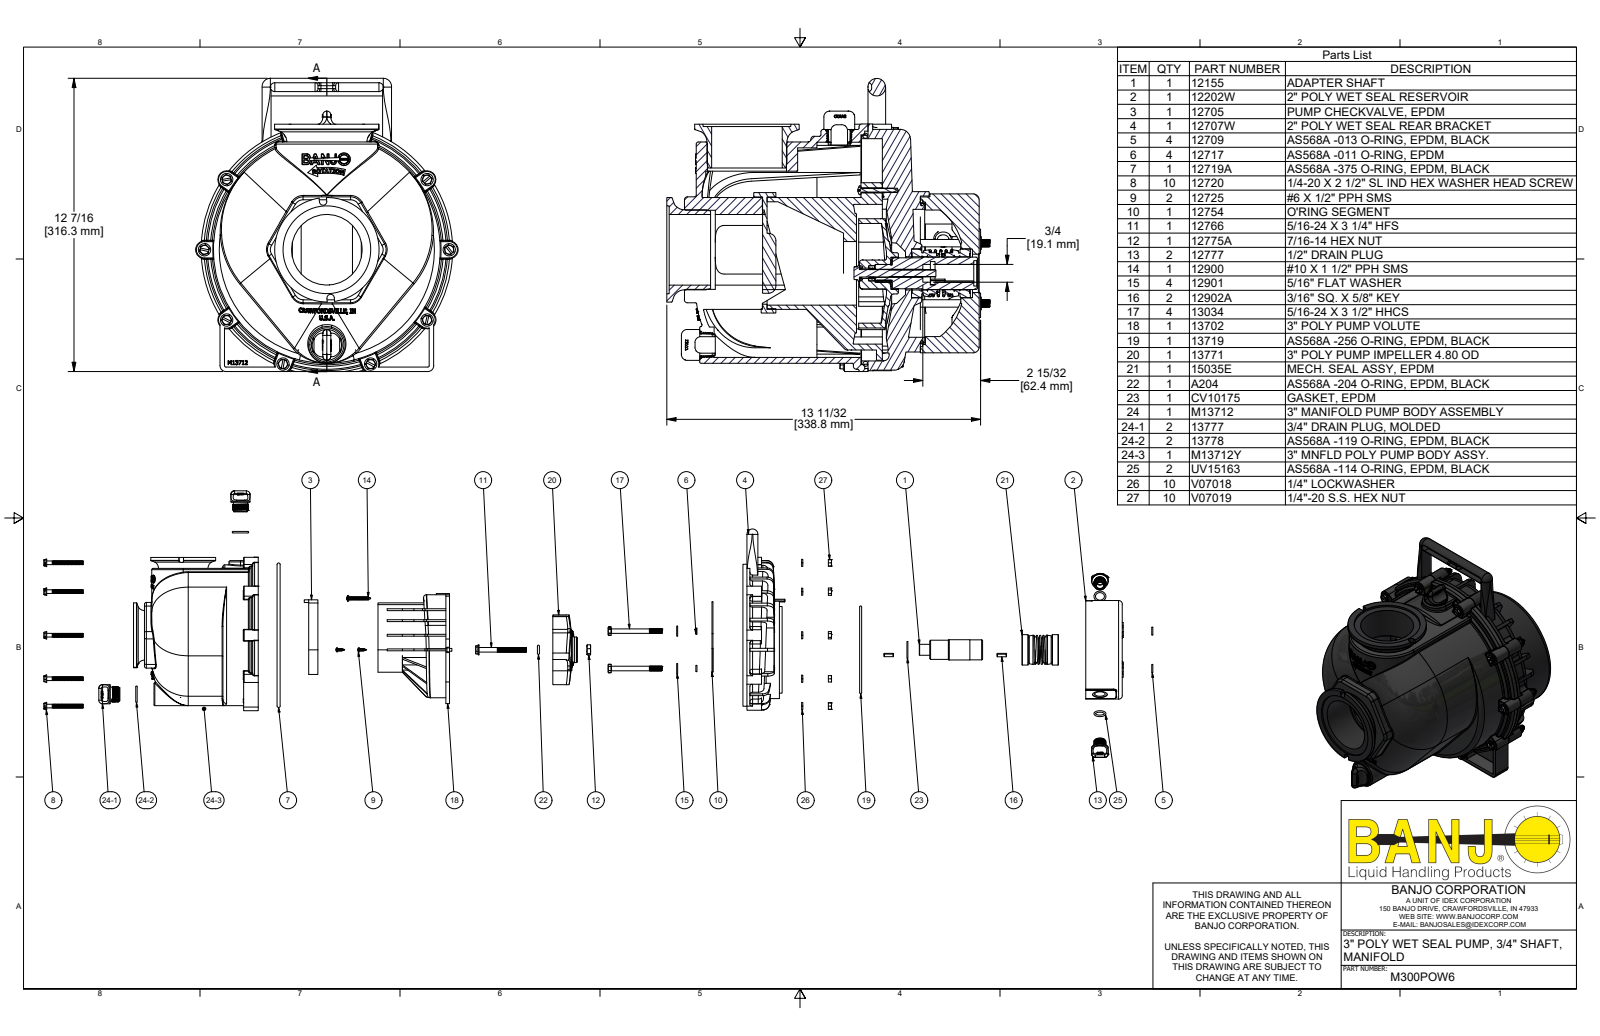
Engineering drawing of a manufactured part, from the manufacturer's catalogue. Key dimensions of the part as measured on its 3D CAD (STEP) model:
Part name (STEP PRODUCT): M300POW6; 12707W; 12707WX; 12703AWV (+8 more)
STEP written by: Autodesk Inventor 2022 (AUTOMOTIVE_DESIGN)
Units: inches
Bodies: 95 solids, 8762 faces (2196 planar, 2270 cylindrical, 4296 other)
Overall size (bounding box): 13.736 × 12.451 × 11.15
Volume: 262.3 in³ · Surface area: 2 140 in²
Round holes (diameter × count): ⌀0.196 ×10, ⌀0.252 ×10, ⌀0.27 ×10, ⌀0.469 ×8, ⌀0.22 ×7, ⌀0.344 ×5, ⌀0.313 ×4, ⌀0.561 ×4, ⌀0.113 ×2, ⌀0.115 ×2, ⌀0.205 ×2, ⌀0.25 ×2
Round bosses / shafts (diameter × count): ⌀0.276 ×80, ⌀0.52 ×10, ⌀0.489 ×10, ⌀0.25 ×10, ⌀0.192 ×8, ⌀0.313 ×5, ⌀0.688 ×4, ⌀0.381 ×4
Partial cylindrical surfaces — rounded edges, fillets, slot ends (radius × count): R0.03 ×138, R0.125 ×76, R0.015 ×61, R0.06 ×51, R0.187 ×35, R0.25 ×27, R0.375 ×16, R2.5 ×16
Main face-to-face distances: 0.25, 1, 4.724, 0.187, 0.125, 0.19, 0.2, 0.163, 2.225, 2.499
Hole centre spacings: 3.087, 5.2, 2.56, 0.69, 1.81, 2.5, 3.535, 4.31
